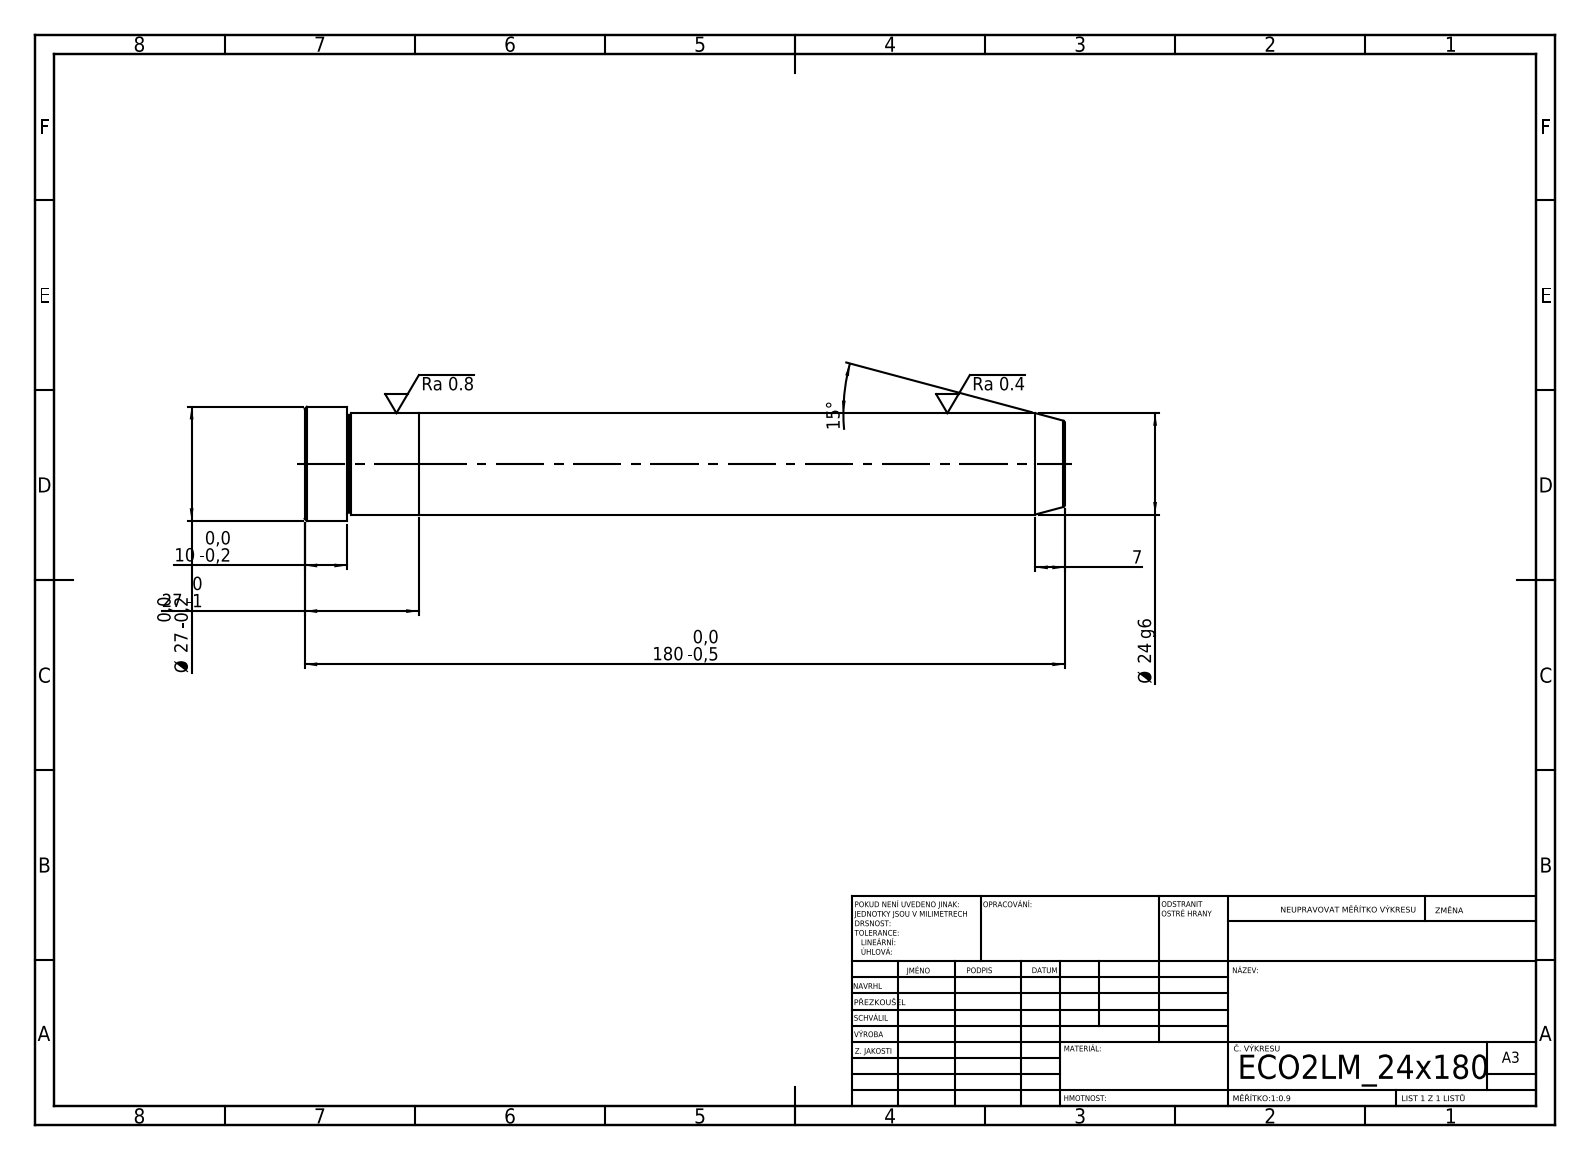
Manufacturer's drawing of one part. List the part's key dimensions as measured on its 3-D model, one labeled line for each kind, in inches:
STEP written by: SolidWorks 2019 (CONFIG_CONTROL_DESIGN)
Units: inches
Bodies: 2 solids, 21 faces (5 planar, 6 cylindrical, 10 other)
Overall size (bounding box): 7.087 × 1.063 × 1.063
Volume: 5.011 in³ · Surface area: 24.13 in²
Round bosses / shafts (diameter × count): ⌀1.063 ×1, ⌀0.945 ×1
Main face-to-face distances: 1.063, 6.024, 7.087, 6.693, 0.669, 0.394
